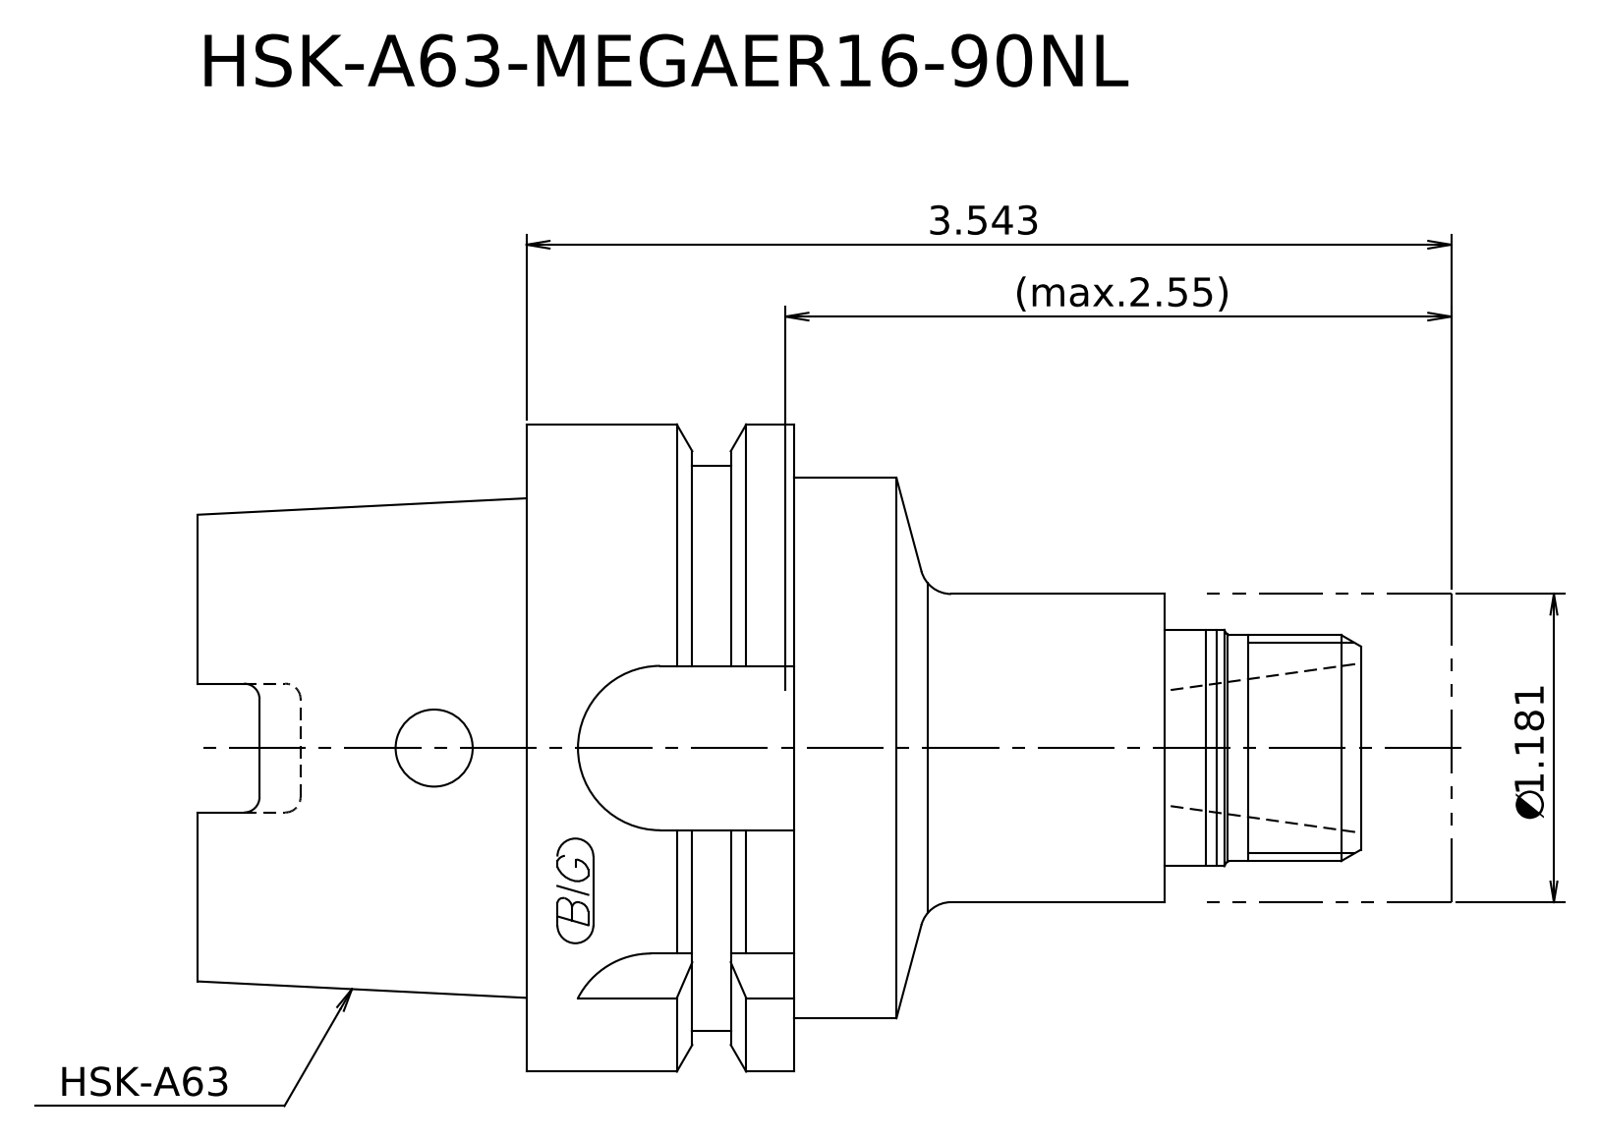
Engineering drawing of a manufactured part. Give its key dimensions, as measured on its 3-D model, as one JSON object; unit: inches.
{"step_written_by": "Kubotek KeyCreator 2011 V10.0.2 (22737) (automotive_design)", "units": "inches", "bodies": {"solids": 2, "faces": 23, "planar": 9, "cylindrical": 8, "other": 6}, "overall_size": [4.803, 2.48, 2.48], "volume_in3": 12.32, "surface_area_in2": 39.72, "round_bosses_or_shafts": [[2.48, 1], [2.165, 1], [2.071, 1], [1.181, 1], [0.906, 1], [0.866, 1]], "face_to_face_distances": [1.26, 1.024, 2.283, 1.535, 2.559, 3.819, 0.984, 2.52, 3.543, 4.803]}
